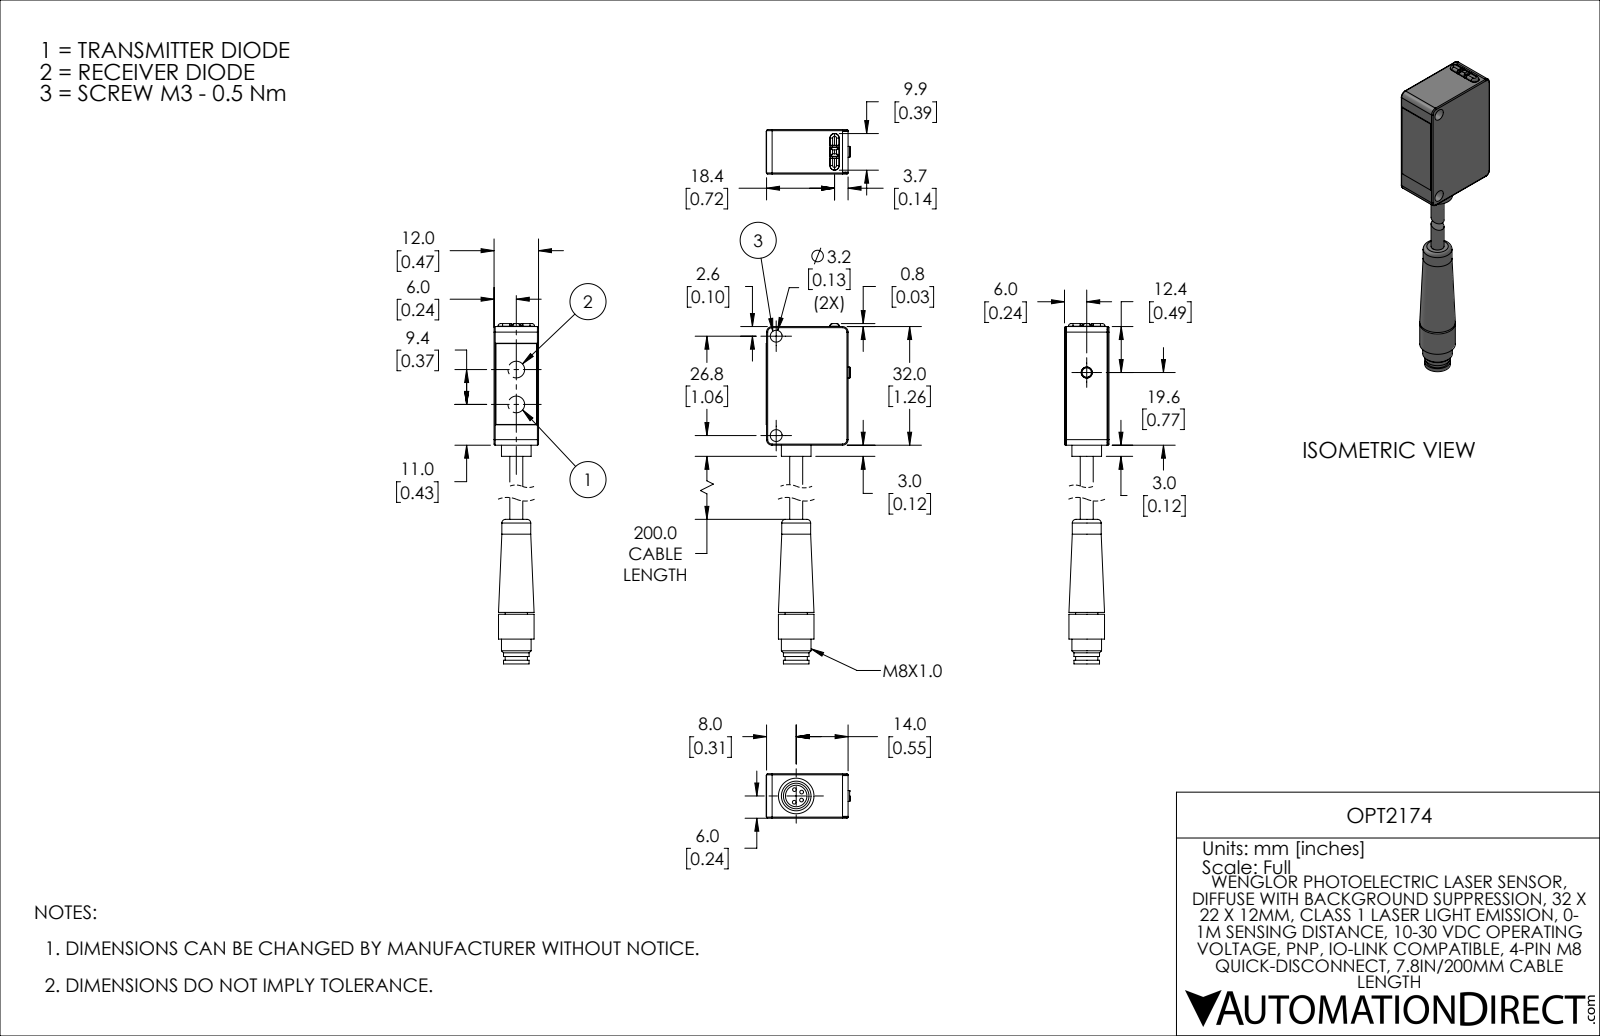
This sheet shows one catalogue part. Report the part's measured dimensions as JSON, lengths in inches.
{"part_name": "OPT2174", "step_written_by": "SolidWorks 2019 (AUTOMOTIVE_DESIGN)", "units": "inches", "bodies": {"solids": 4, "faces": 203, "planar": 96, "cylindrical": 74, "other": 33}, "overall_size": [3.602, 1.245, 0.472], "volume_in3": 0.651, "surface_area_in2": 7.486, "round_holes": [[0.126, 2], [0.083, 1], [0.118, 1], [0.228, 1]], "round_bosses_or_shafts": [[0.039, 4], [0.008, 2], [0.378, 1], [0.315, 1], [0.307, 1], [0.272, 1], [0.236, 1], [0.138, 1]], "partial_cylinders_radius": [[0.012, 12], [0.028, 6], [0.02, 4], [0.059, 4], [0.004, 2], [0.048, 2], [0.049, 2], [0.075, 1]], "face_to_face_distances": [0.472, 0.87, 1.26, 0.02, 0.866, 0.016, 0.453, 0.457, 0.437, 0.118], "hole_center_spacings": [1.055]}
